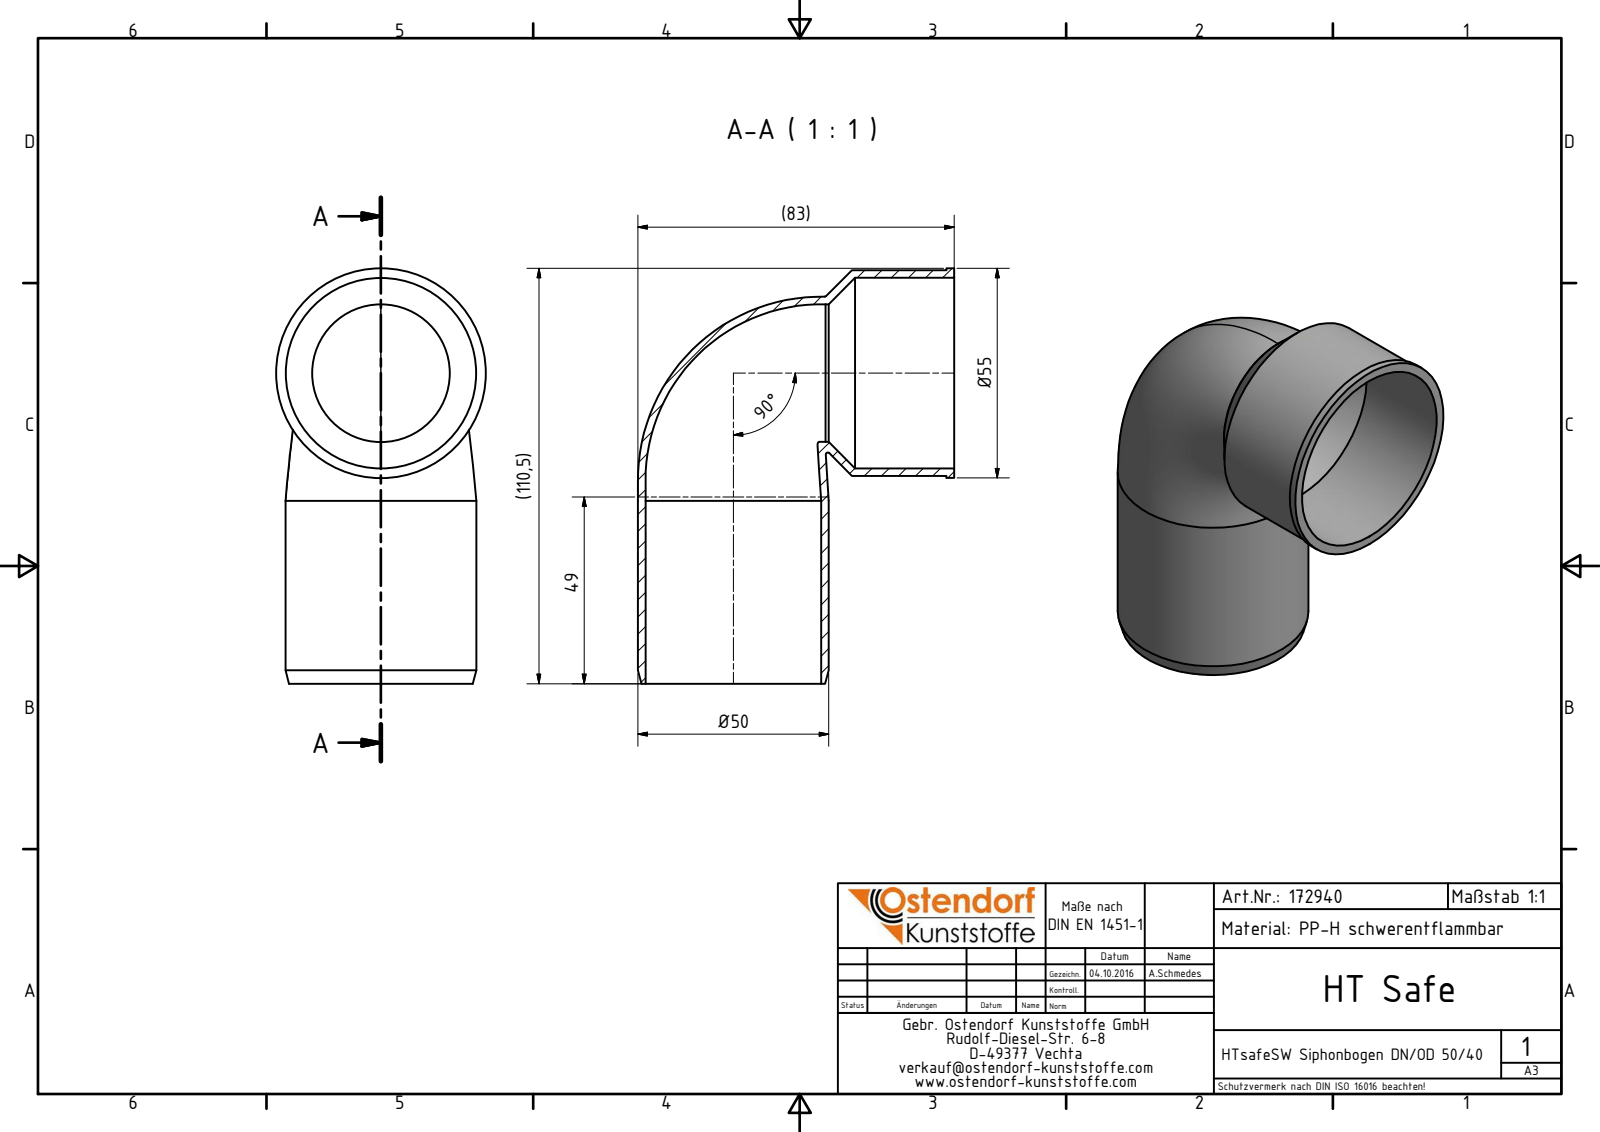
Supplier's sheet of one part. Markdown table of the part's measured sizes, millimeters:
| quantity | value |
| --- | --- |
| part name | 172940 HTsafeSW DN_OD 50_40 |
| STEP written by | Autodesk Inventor 2016 (AUTOMOTIVE_DESIGN) |
| units | millimeters |
| bodies | 1 solid, 15 faces (3 planar, 6 cylindrical, 6 other) |
| overall size | 109 × 83.05 × 55 |
| volume | 38 876 mm³ |
| surface area | 39 571 mm² |
| round holes (diameter × count) | 36.1 × 1, 46.1 × 1, 50 × 1 |
| round bosses / shafts (diameter × count) | 55 × 1, 54 × 1, 50.1 × 1 |
| main face-to-face distances | 2 |
